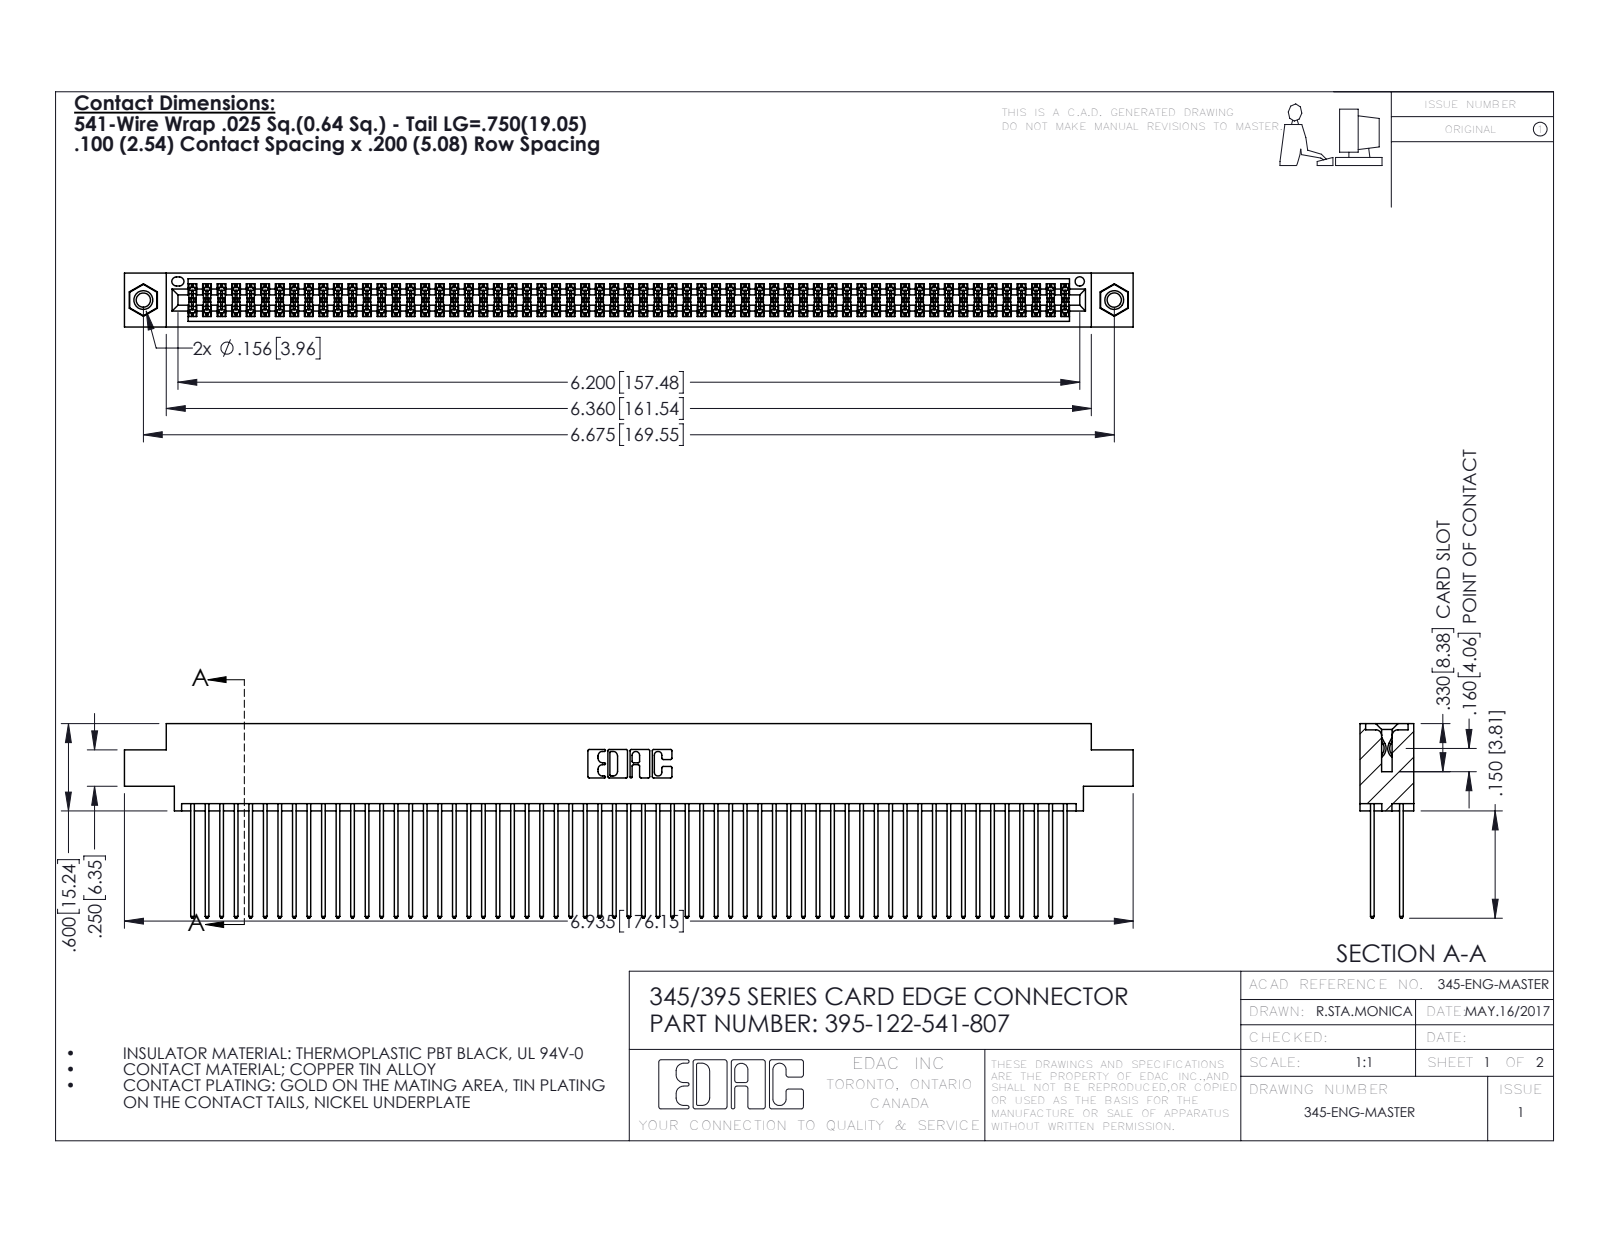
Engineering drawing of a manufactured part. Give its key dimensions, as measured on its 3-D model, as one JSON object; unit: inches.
{"part_name": "395-122-541-807; 345 Part_0.170 Offset - 0.156 Dia-TI; 345-250-001_345-250-005-103; 345-292-001_345-293-141", "step_written_by": "SolidWorks 2016 (CONFIG_CONTROL_DESIGN)", "units": "inches", "bodies": {"solids": 125, "faces": 6290, "planar": 4142, "cylindrical": 2132, "other": 16}, "overall_size": [6.935, 1.337, 0.37], "volume_in3": 1.09, "surface_area_in2": 46.86, "round_holes": [[0.098, 2], [0.125, 2], [0.156, 2], [0.064, 1]], "round_bosses_or_shafts": [[0.155, 2]], "partial_cylinders_radius": [[0.006, 183], [0.01, 122], [0.01, 22], [0.007, 6], [0.031, 6], [0.026, 3], [0.014, 2], [0.019, 2]], "face_to_face_distances": [0.072, 0.298, 0.2, 0.098, 0.272, 0.025, 0.225, 0.37, 0.175, 0.149], "hole_center_spacings": [0.27, 6.439, 6.675]}
